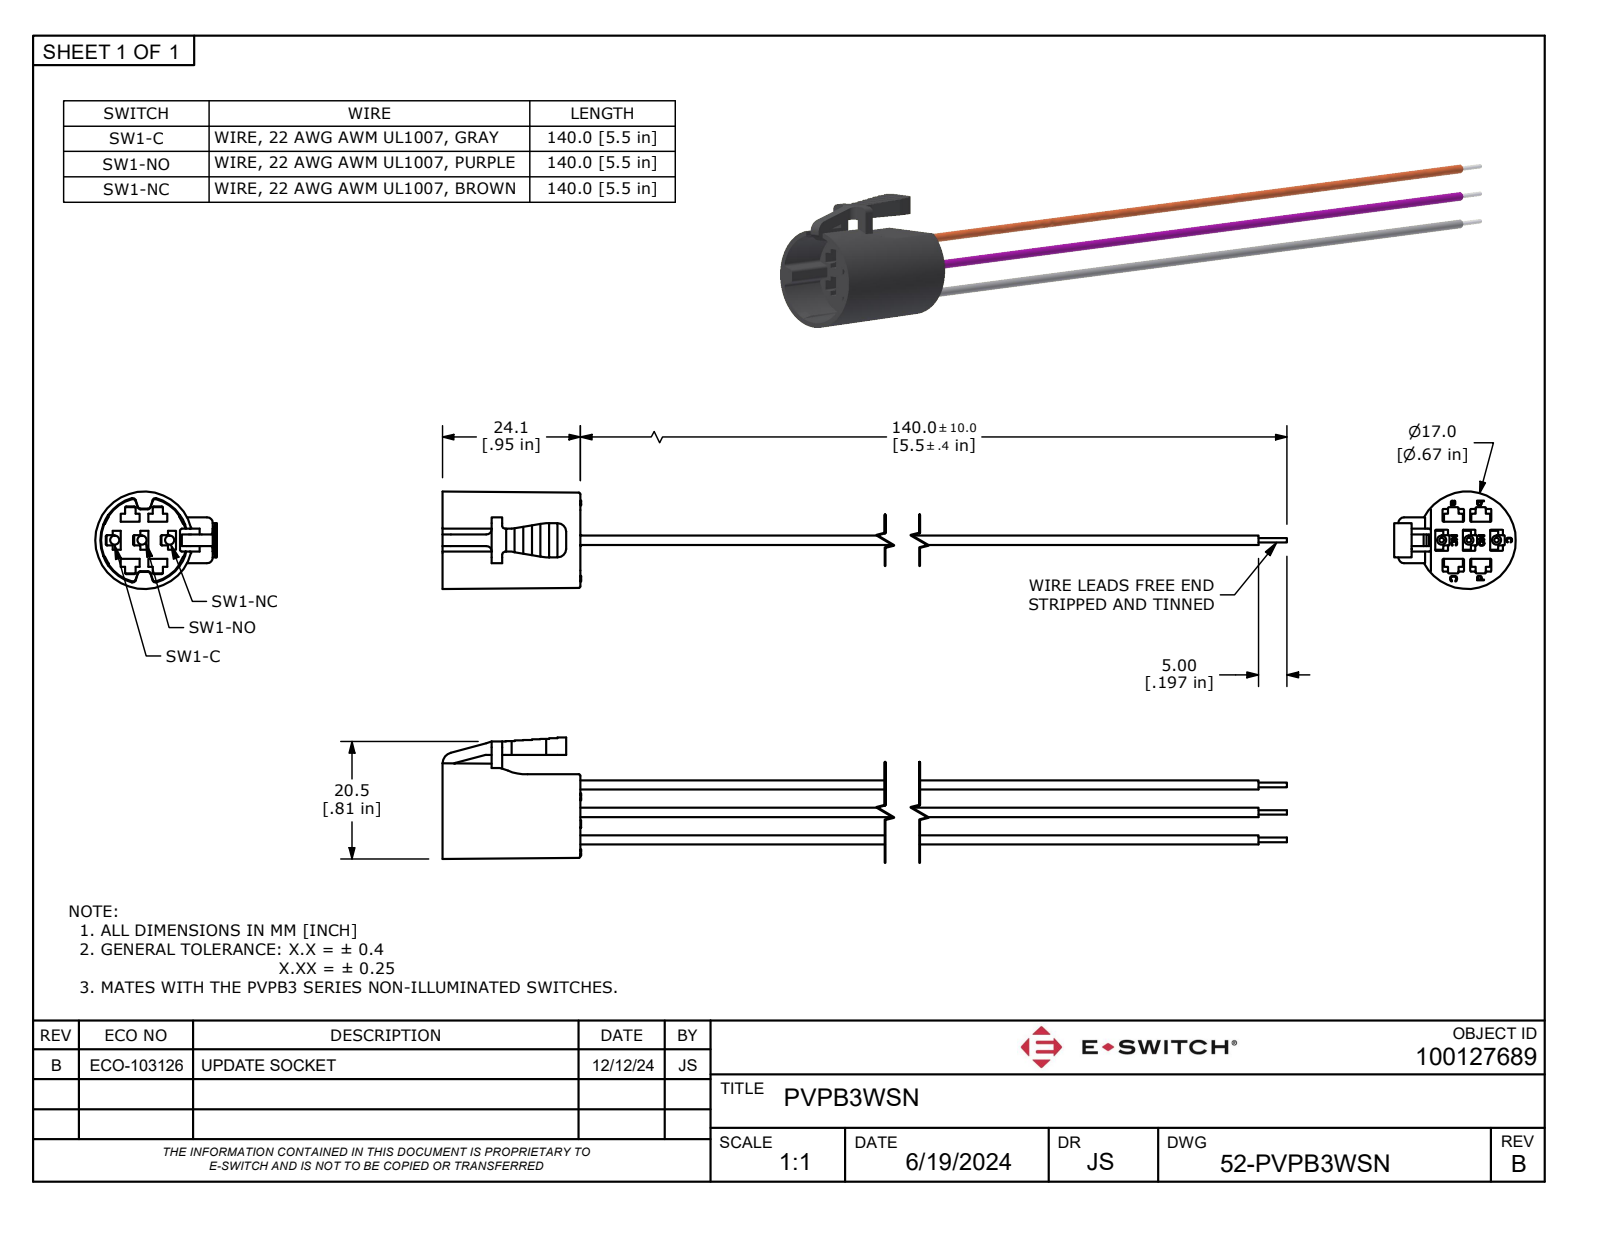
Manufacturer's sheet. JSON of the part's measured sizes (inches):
{"part_name": "PVPB3WSN", "step_written_by": "Autodesk Inventor 2022 (AUTOMOTIVE_DESIGN)", "units": "inches", "bodies": {"solids": 4, "faces": 717, "planar": 551, "cylindrical": 6, "other": 160}, "overall_size": [6.461, 0.835, 0.67], "volume_in3": 0.189, "surface_area_in2": 8.861, "round_bosses_or_shafts": [[0.063, 3], [0.031, 3]], "face_to_face_distances": [0.189, 0.61, 0.146, 0.03, 0.197, 0.175, 0.201, 0.055, 0.159, 0.087]}
